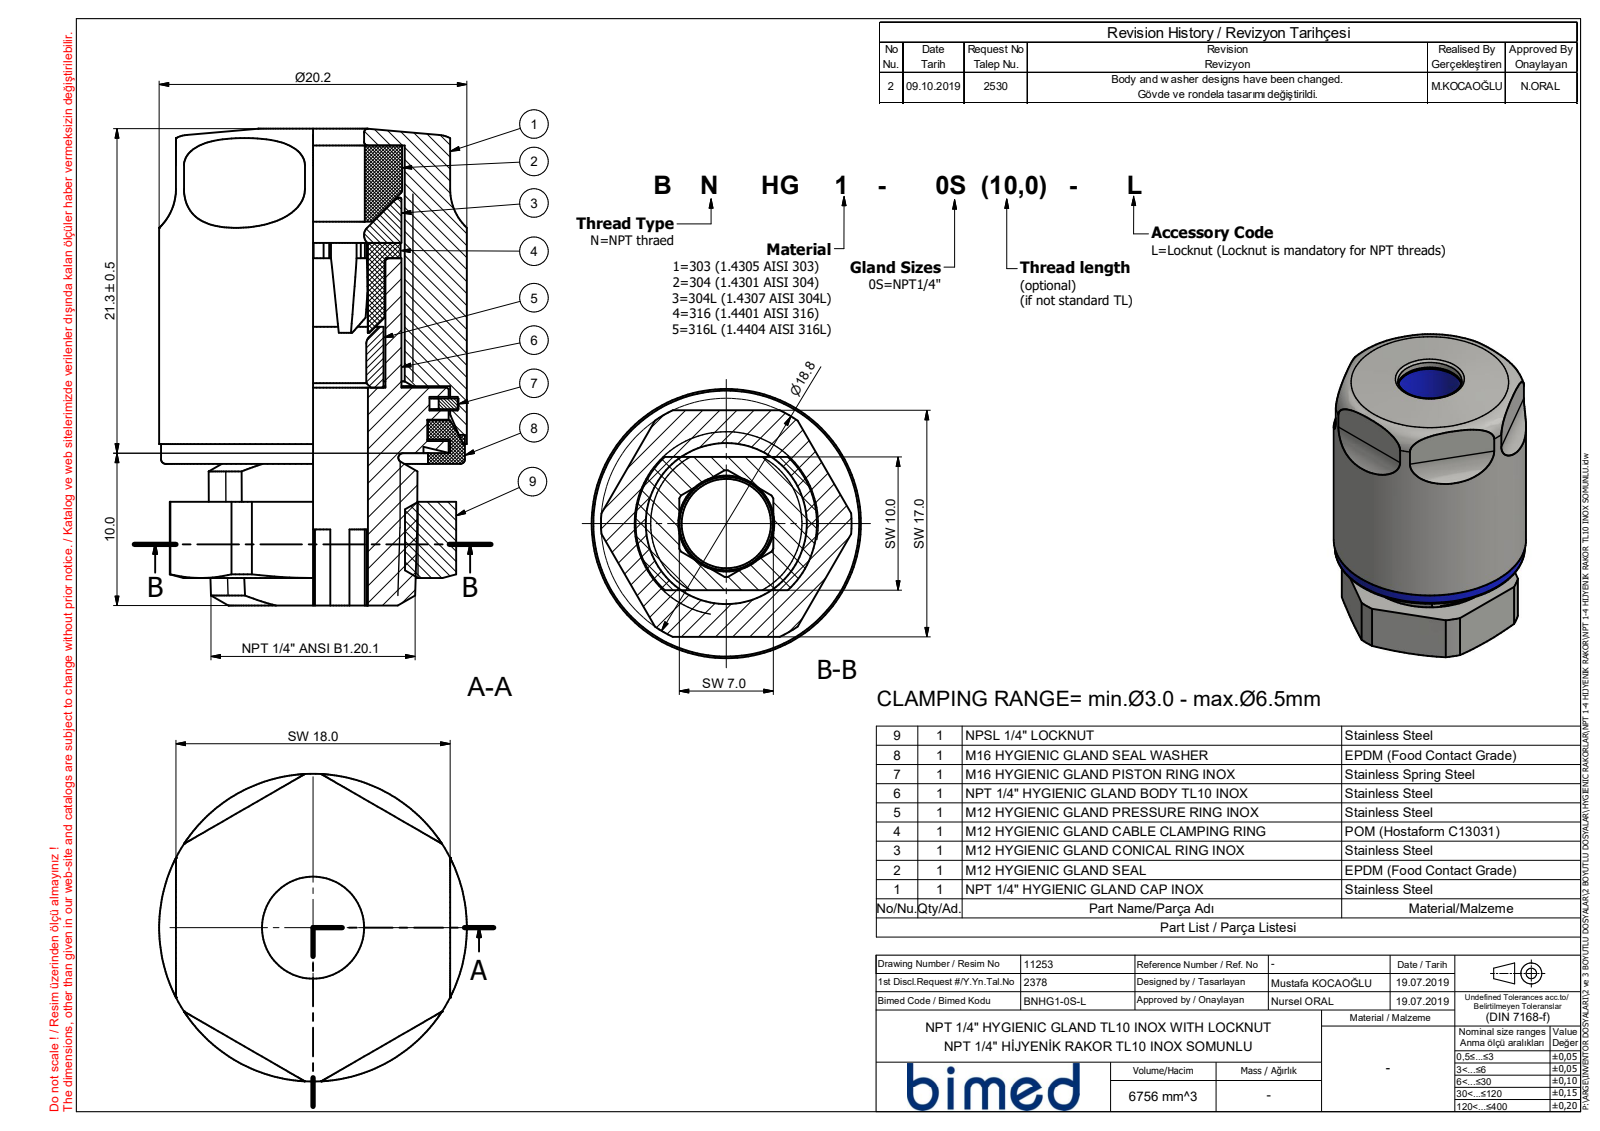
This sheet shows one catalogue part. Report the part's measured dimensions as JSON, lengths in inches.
{"part_name": "BNHG1-0S-L", "step_written_by": "SolidWorks 2021 (CONFIG_CONTROL_DESIGN)", "units": "inches", "bodies": {"solids": 1, "faces": 53, "planar": 15, "cylindrical": 10, "other": 28}, "overall_size": [1.245, 0.795, 0.795], "volume_in3": 0.529, "surface_area_in2": 4.139, "round_bosses_or_shafts": [[0.795, 1], [0.785, 1]], "partial_cylinders_radius": [[0.37, 1]], "face_to_face_distances": [0.098, 0.669, 0.197, 0.295, 0.071, 0.268, 0.366, 0.138, 0.531, 0.394]}
